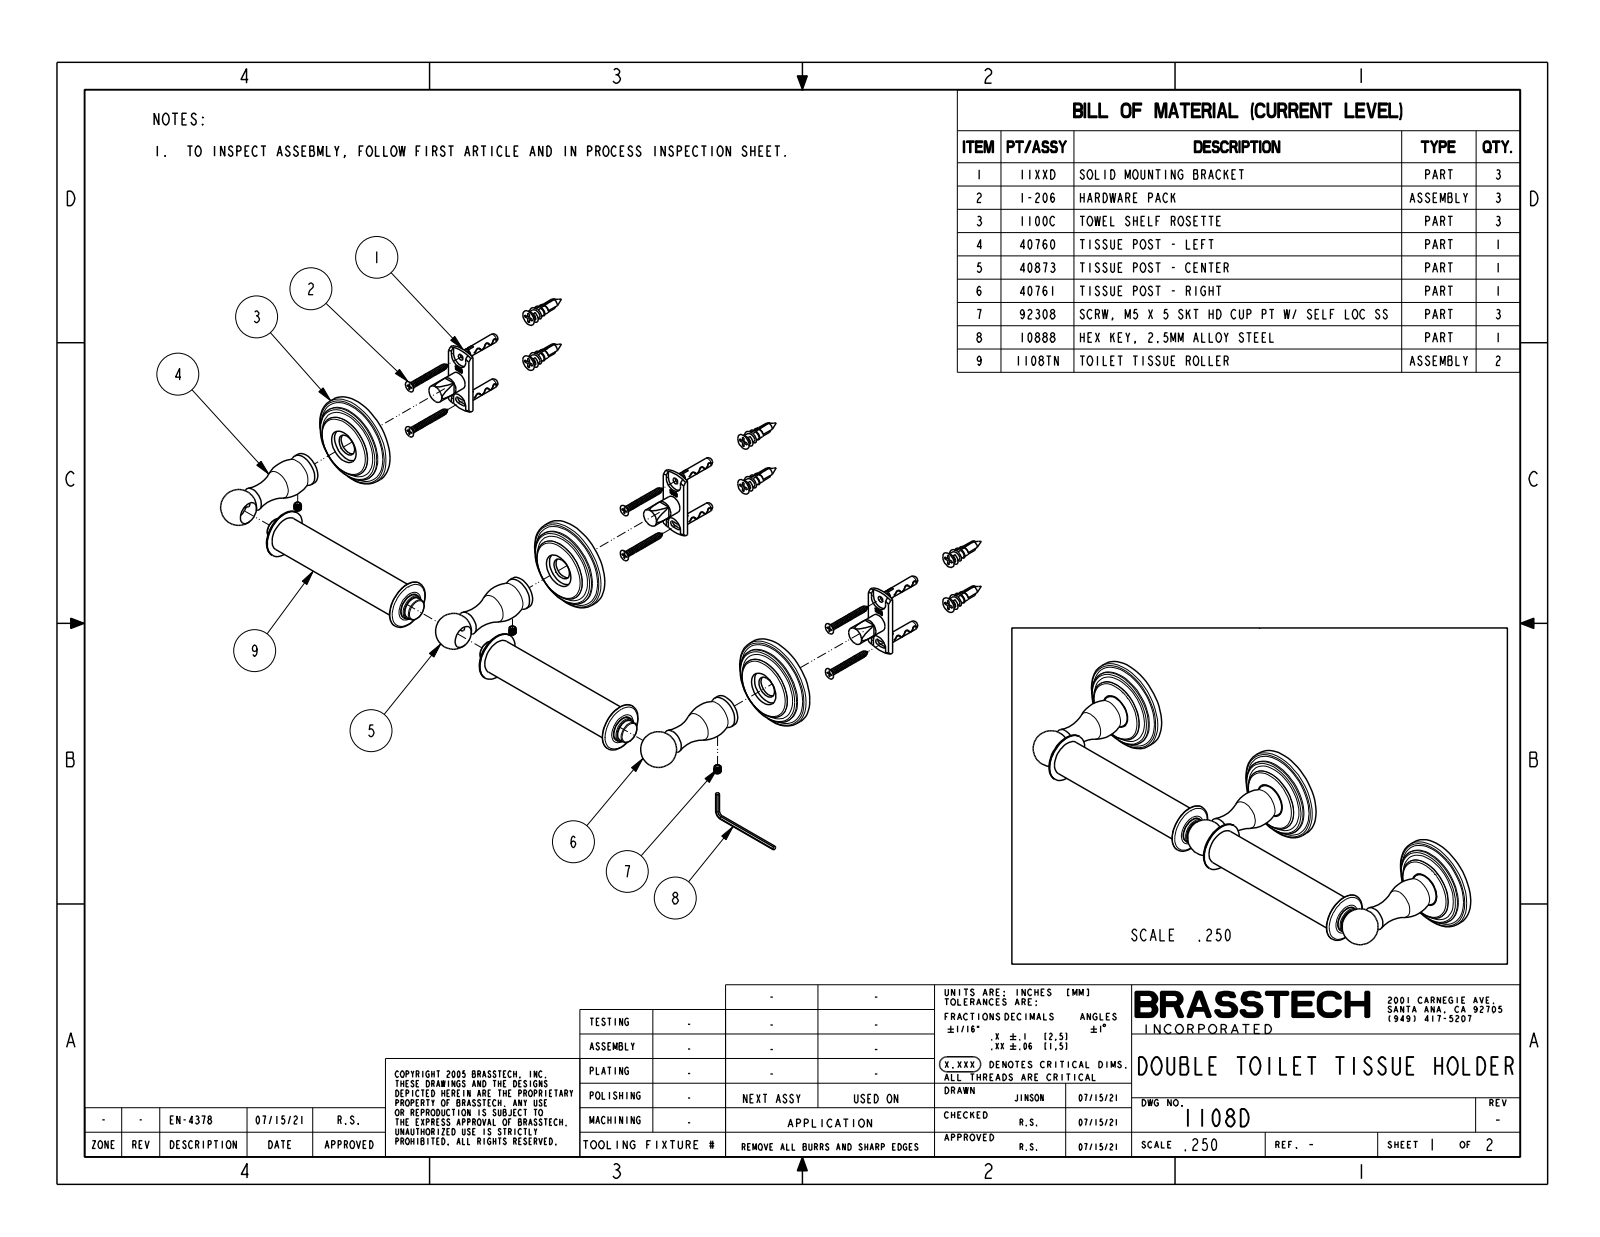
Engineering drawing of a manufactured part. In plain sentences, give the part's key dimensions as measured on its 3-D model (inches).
The part is named "1108D". Its 3-D file was written by "CREO PARAMETRIC BY PTC INC, 2018400 (CONFIG_CONTROL_DESIGN)". It is 1 solid with 170 faces: 28 planar, 50 cylindrical and 92 other. Overall it measures 14.56 by 3.691 by 2.56 inches. Its volume is 18.24 cubic inches and its surface area 98.05 square inches. Round holes: 1 of diameter 0.63. Round bosses or shafts: 3 of diameter 2.56, 3 of diameter 2.182, 3 of diameter 1.748, 1 of diameter 1.358, 1 of diameter 1.358, 1 of diameter 0.984, 1 of diameter 0.701, 1 of diameter 0.693. The main face-to-face distances are 0.512, 0.362, 0.15, 6, 4.75, 0.189, 0.173, 0.323, 10.75, 1.25.
